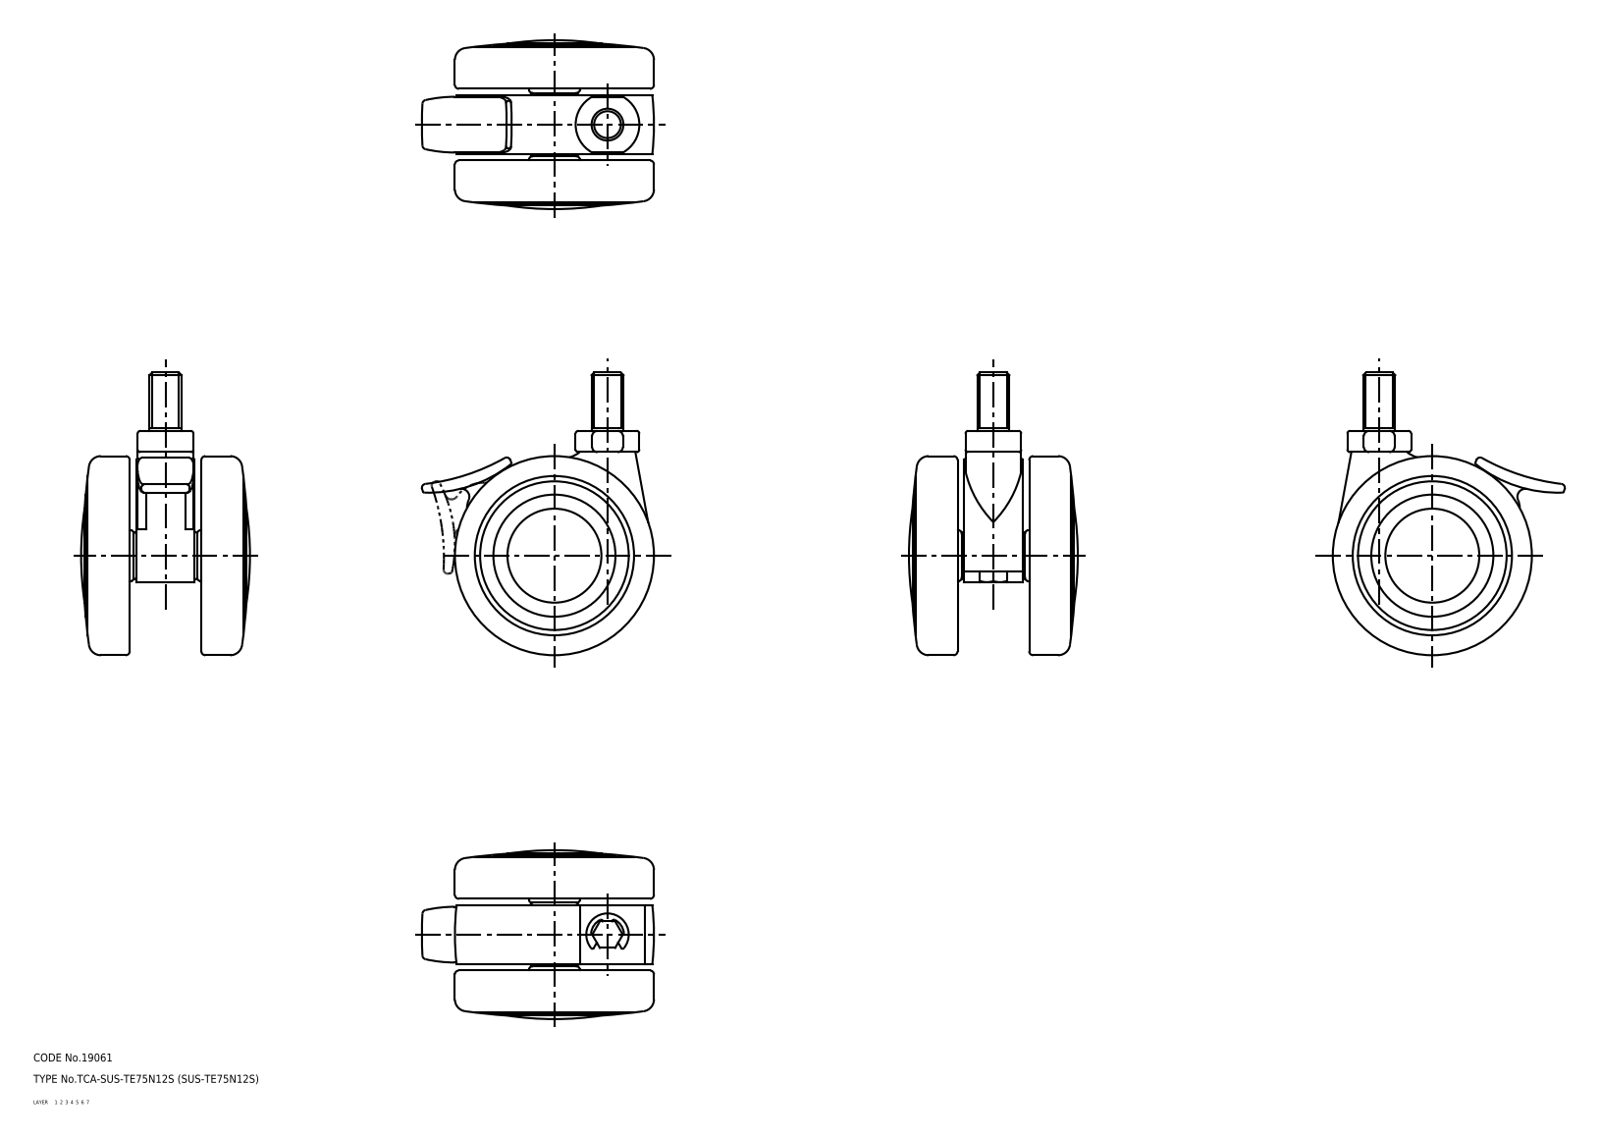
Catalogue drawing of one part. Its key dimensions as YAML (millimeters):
part_name: "lever; wheel_mr; wheel; main shaft (+1 more)"
step_written_by: "CADfix (AUTOMOTIVE_DESIGN)"
units: millimeters
bodies: {solids: 5, faces: 195, planar: 0, cylindrical: 0, other: 195}
overall_size: [106.5, 87.44, 63.62]
volume: 202741
surface_area: 51851
